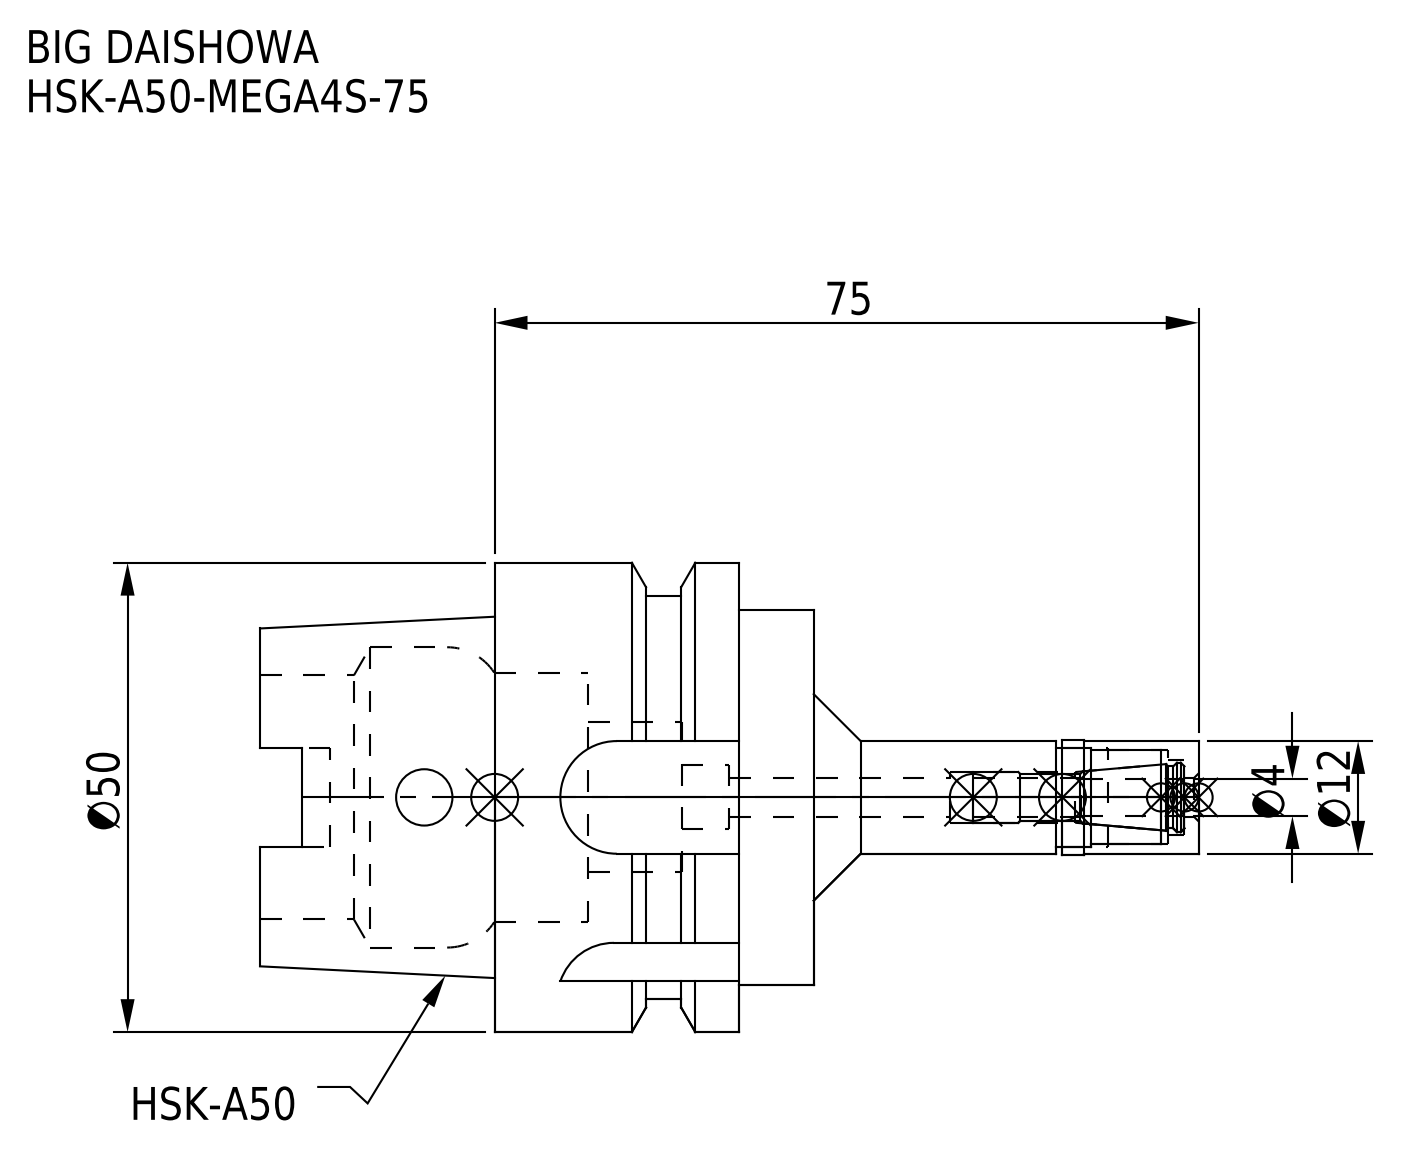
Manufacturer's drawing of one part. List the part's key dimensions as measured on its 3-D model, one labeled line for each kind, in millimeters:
Part name (STEP PRODUCT): HSK-A50-MEGA4S-75_1.stp; MGN4S_1.stp; DXF_TEMP_ASSY_ASM_4_ASM.stp; HSK-A50-MEGA4S-75-040.stp (+3 more)
STEP written by: SolidWorks 2019 (CONFIG_CONTROL_DESIGN)
Units: millimetres
Bodies: 2 solids, 122 faces (47 planar, 55 cylindrical, 20 other)
Overall size (bounding box): 100 × 50 × 50
Volume: 63 232 mm³ · Surface area: 19 302 mm²
Round holes (diameter × count): ⌀4.1 ×1, ⌀4.2 ×1, ⌀5.4 ×1, ⌀6 ×1, ⌀6.8 ×1, ⌀8 ×1, ⌀10 ×1, ⌀10.5 ×1, ⌀16 ×1, ⌀26 ×1, ⌀26.6 ×1, ⌀32 ×1
Round bosses / shafts (diameter × count): ⌀50 ×1, ⌀43 ×1, ⌀40 ×1, ⌀12.3 ×1, ⌀12 ×1
Partial cylindrical surfaces — rounded edges, fillets, slot ends (radius × count): R2.38 ×4, R6 ×4
Main face-to-face distances: 34, 8, 26, 24.05, 16.05, 9.95, 25, 59, 51, 34.95
